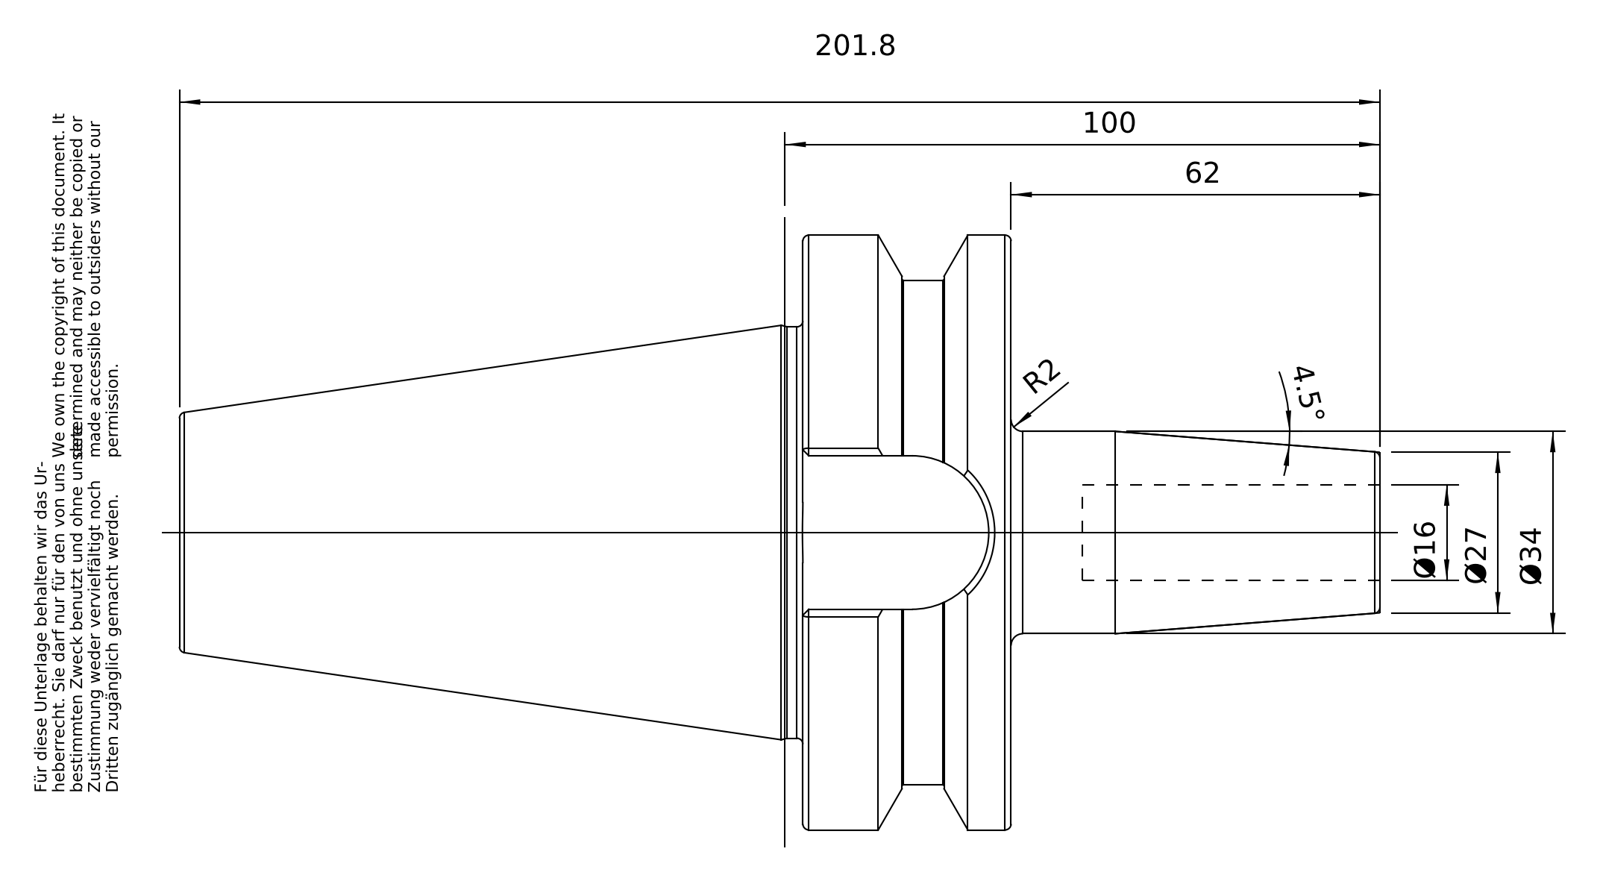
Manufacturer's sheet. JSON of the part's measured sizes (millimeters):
{"part_name": "50-640-16", "step_written_by": "PRO/ENGINEER BY PARAMETRIC TECHNOLOGY CORPORATION, 2010430 (CONFIG_CONTROL_DESIGN)", "units": "millimeters", "bodies": {"solids": 1, "faces": 96, "planar": 26, "cylindrical": 22, "other": 48}, "overall_size": [201.8, 99.97, 99.97], "volume_mm3": 506621, "surface_area_mm2": 60052, "round_holes": [[16, 1], [20.75, 1], [25.02, 1], [25.7, 1]], "round_bosses_or_shafts": [[99.97, 1], [84.75, 1], [69.15, 1], [34, 1], [24.01, 1]], "partial_cylinders_radius": [[12.9, 1]], "face_to_face_distances": [35, 70.4, 104.8, 139.8, 25.8, 201.8, 97, 62, 151.8, 47]}
